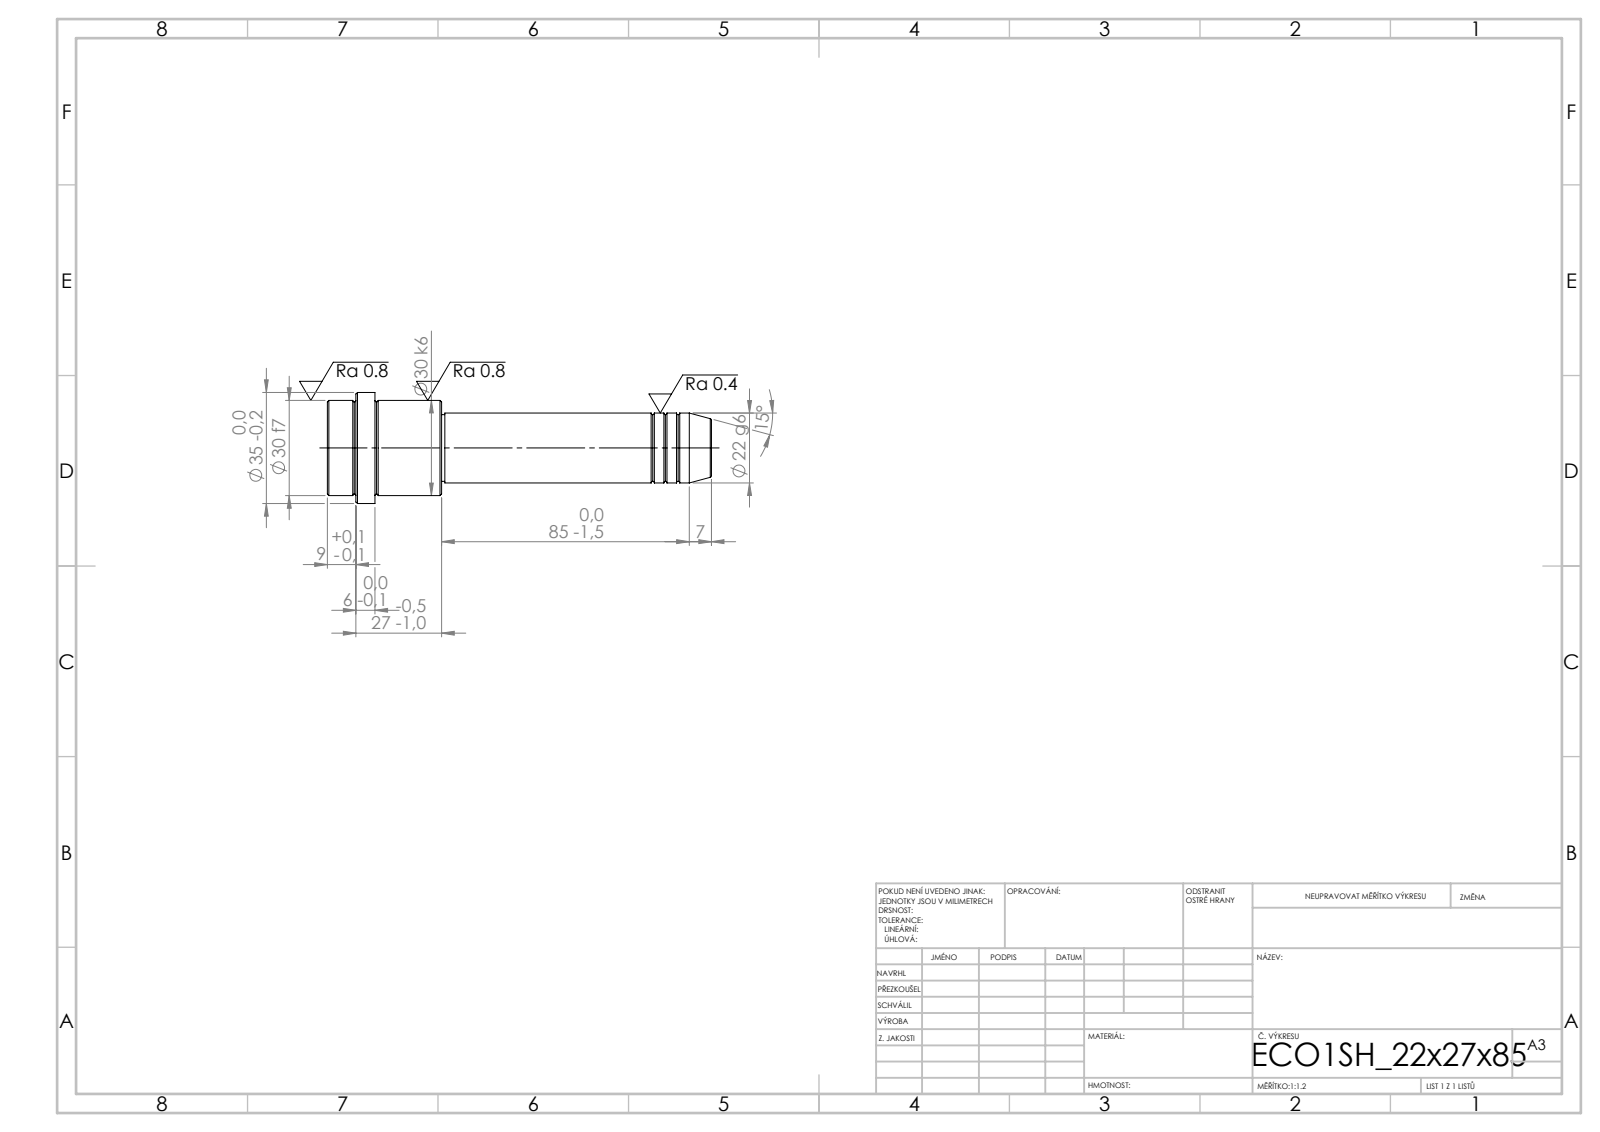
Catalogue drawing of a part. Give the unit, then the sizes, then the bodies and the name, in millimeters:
Units: millimetres
Overall size (bounding box): 121 × 35 × 35
Round bosses / shafts (diameter × count): ⌀35 ×1, ⌀30 ×1, ⌀22 ×1, ⌀21 ×1
Main face-to-face distances: 36, 21, 15, 85, 106, 121, 112, 27, 6, 9
Volume: 58 637 mm³ · Surface area: 11 322 mm²
Bodies: 1 solid, 52 faces (6 planar, 16 cylindrical, 30 other)
STEP written by: SolidWorks 2019 (CONFIG_CONTROL_DESIGN)
